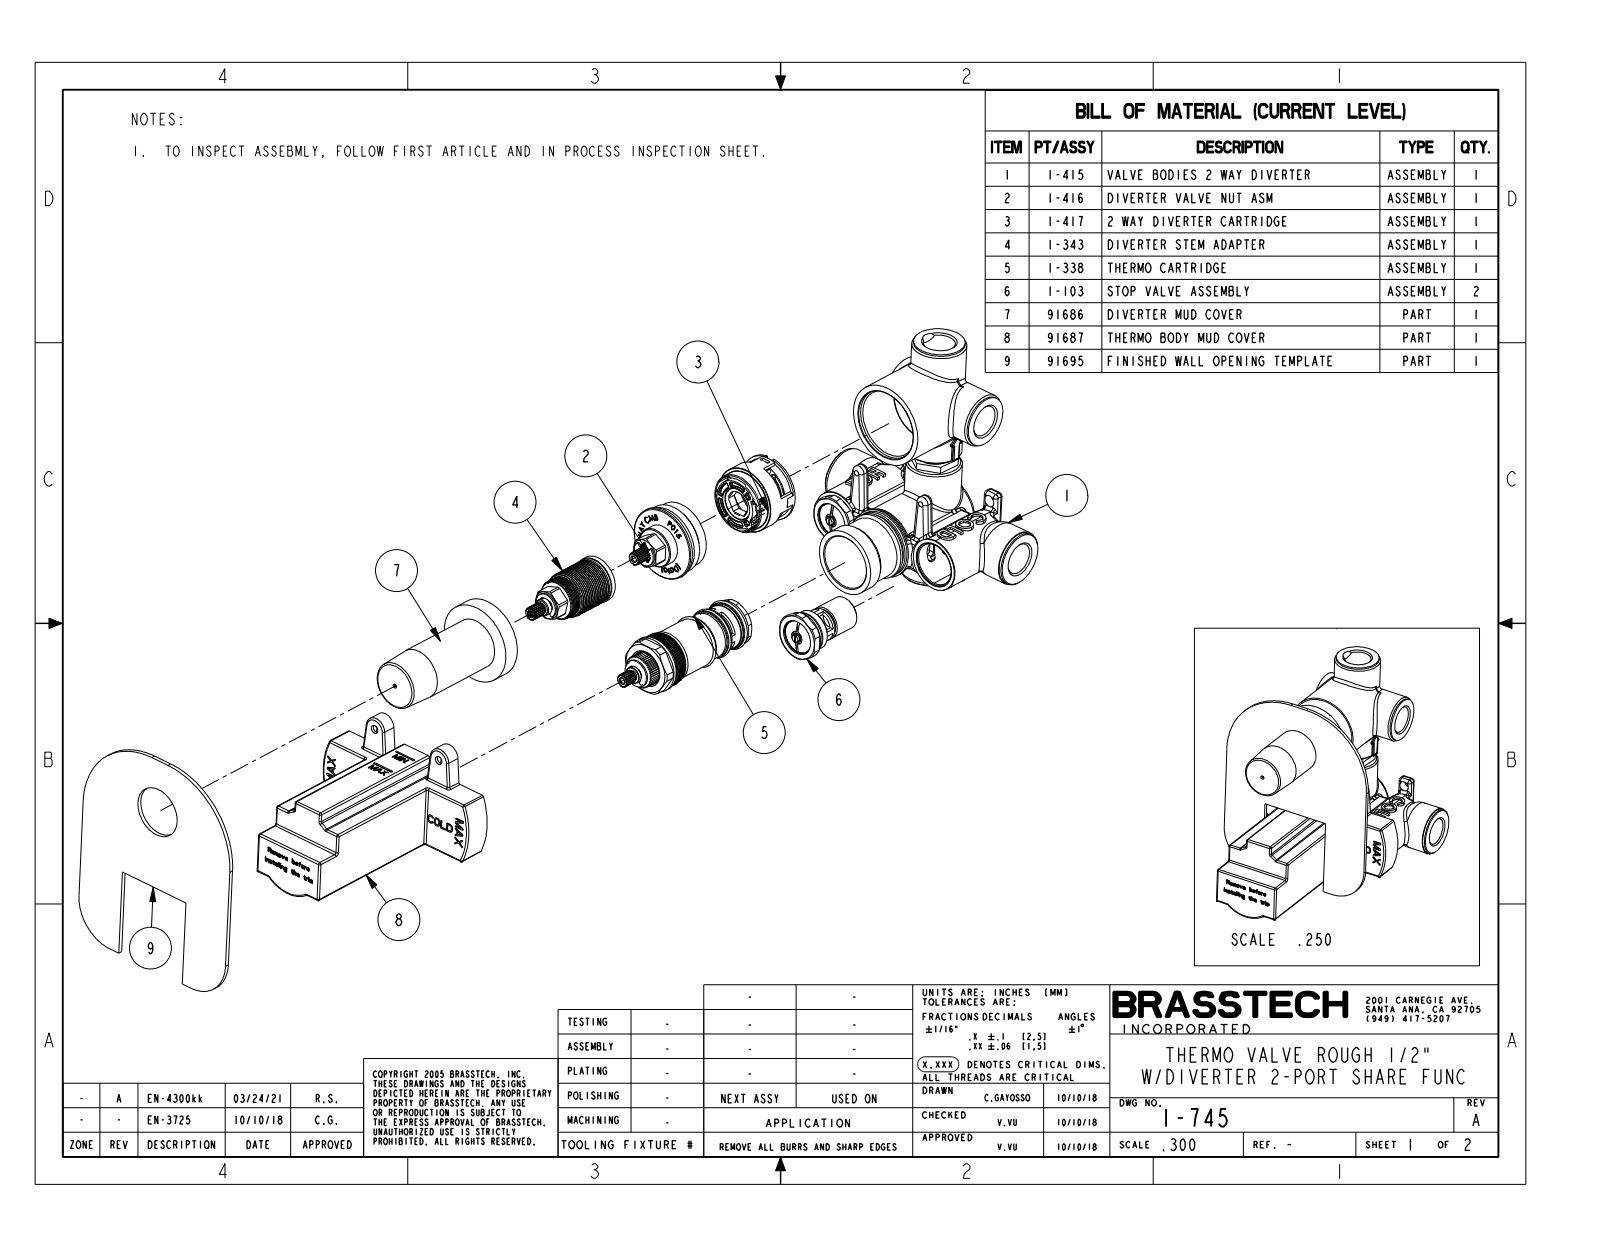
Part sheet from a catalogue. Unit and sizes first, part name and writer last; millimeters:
Units: millimetres
Overall size (bounding box): 159.5 × 138 × 121.8
Round holes (diameter × count): ⌀3.3 ×4, ⌀7 ×2, ⌀8 ×2, ⌀17.6 ×2, ⌀20.5 ×2, ⌀21 ×2, ⌀10 ×1
Round bosses / shafts (diameter × count): ⌀32 ×3, ⌀33 ×2, ⌀30 ×2, ⌀24 ×2, ⌀19.9 ×2, ⌀15.2 ×2, ⌀6.5 ×2, ⌀6 ×2
Partial cylindrical surfaces — rounded edges, fillets, slot ends (radius × count): R2 ×43, R0.5 ×39, R1 ×4, R1.8 ×2, R3.9 ×2, R4 ×2, R5.3 ×2, R7.5 ×2
Main face-to-face distances: 2, 47.5, 44, 27.5, 54.5, 7, 27, 94, 107, 8
Hole centre spacings: 17.2, 21.2, 37.3, 38, 40.8, 43, 51.5, 61.6
Volume: 460 300 mm³ · Surface area: 65 290 mm²
Bodies: 1 solid, 1888 faces (940 planar, 395 cylindrical, 553 other)
Part name (STEP PRODUCT): DEFAULT_REP_SW0001
STEP written by: CREO PARAMETRIC BY PTC INC, 2018400 (CONFIG_CONTROL_DESIGN)
